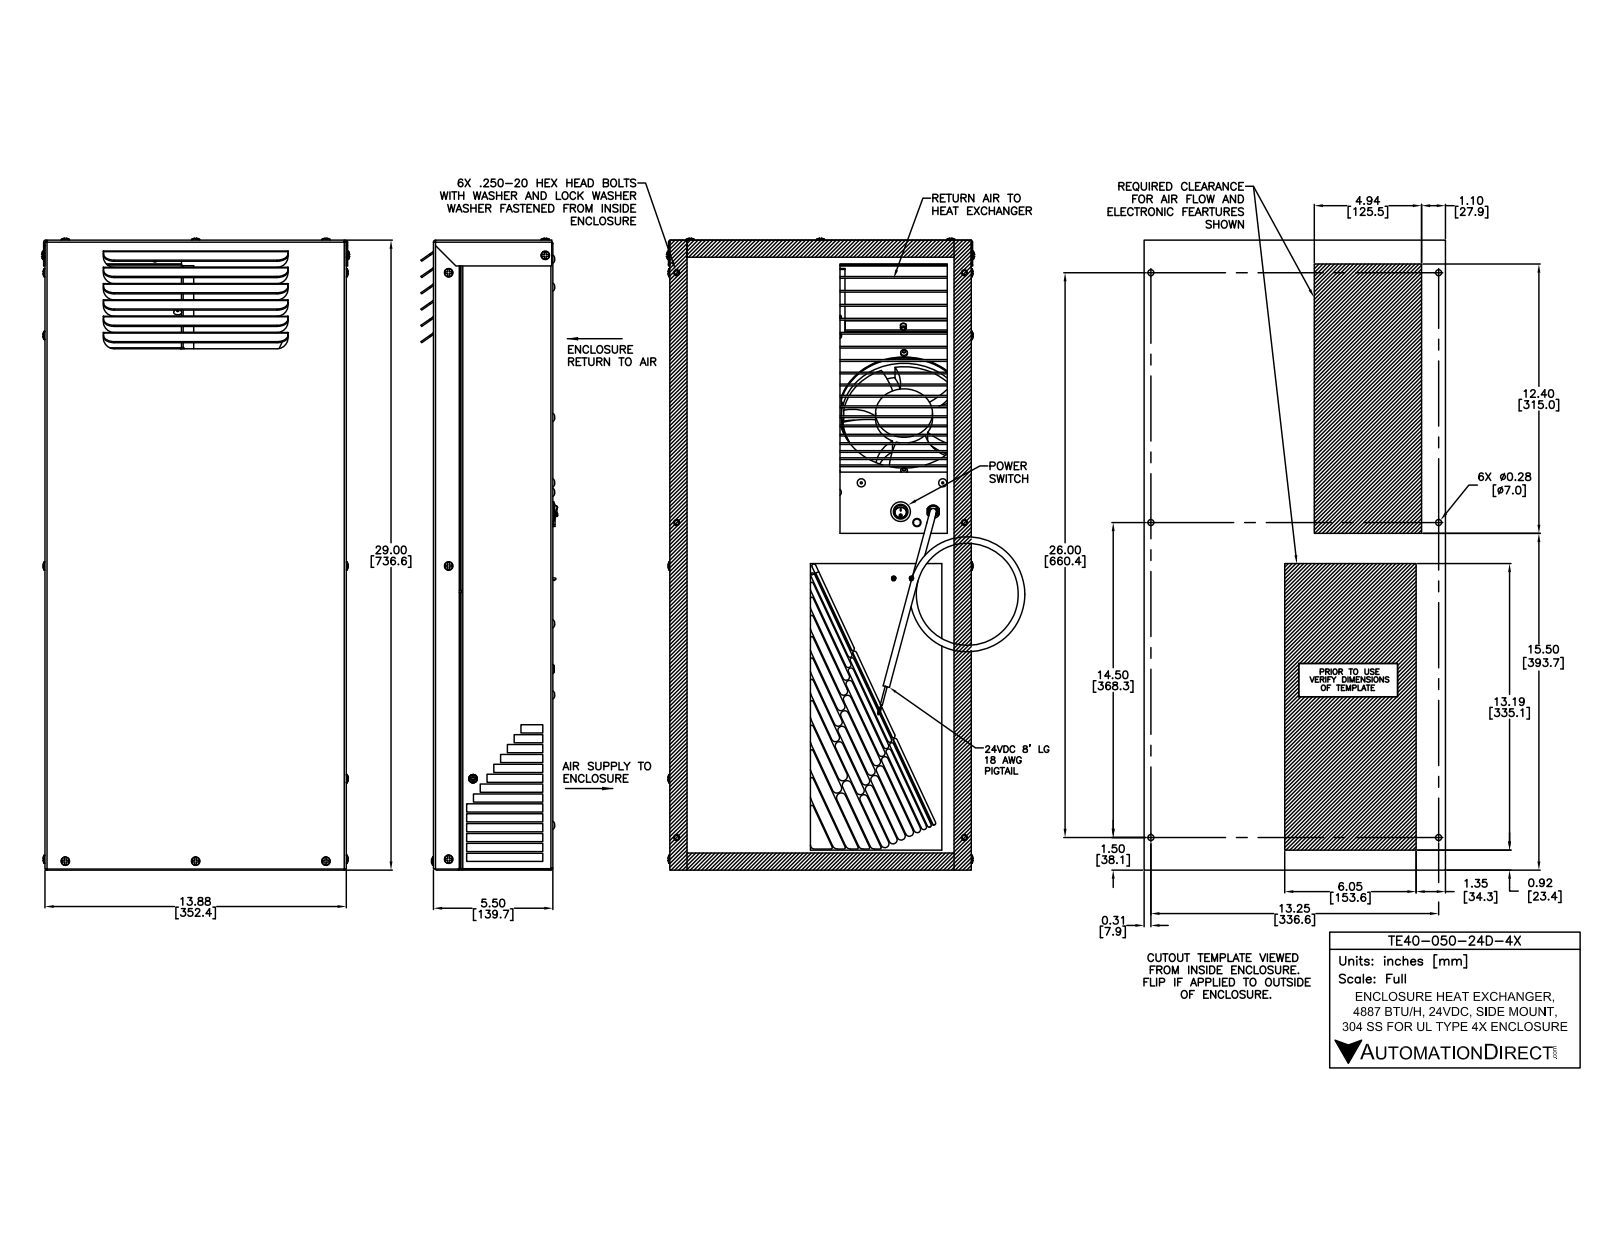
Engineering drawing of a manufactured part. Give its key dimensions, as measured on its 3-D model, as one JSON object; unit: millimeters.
{"part_name": "TE40-050-24D-4X", "step_written_by": "SolidWorks 2017 (AUTOMOTIVE_DESIGN)", "units": "millimeters", "bodies": {"solids": 125, "faces": 3479, "planar": 1943, "cylindrical": 1134, "other": 402}, "overall_size": [739, 419.1, 241.5], "volume_mm3": 5545000, "surface_area_mm2": 3398000, "round_holes": [[4.9, 21], [5.6, 17], [4.8, 15], [4, 14], [5.2, 11], [13.1, 9], [2.8, 8], [4.4, 8], [12.7, 8], [22.5, 8], [5.1, 6], [6.9, 6]], "round_bosses_or_shafts": [[6.9, 15], [4.8, 14], [25.4, 8], [23.7, 8], [14.3, 6], [8.3, 6], [8.3, 6], [6.3, 6]], "partial_cylinders_radius": [[0.3, 96], [0.4, 96], [0.8, 46], [2.4, 46], [1.5, 28], [1.2, 24], [4.8, 19], [1.6, 17]], "face_to_face_distances": [1.6, 1.6, 139.7, 138.1, 136.6, 138.1, 350.9, 6.4, 158.8, 192.1], "hole_center_spacings": [31.8, 63.5, 95.3, 81, 81, 81, 73.6, 162]}
